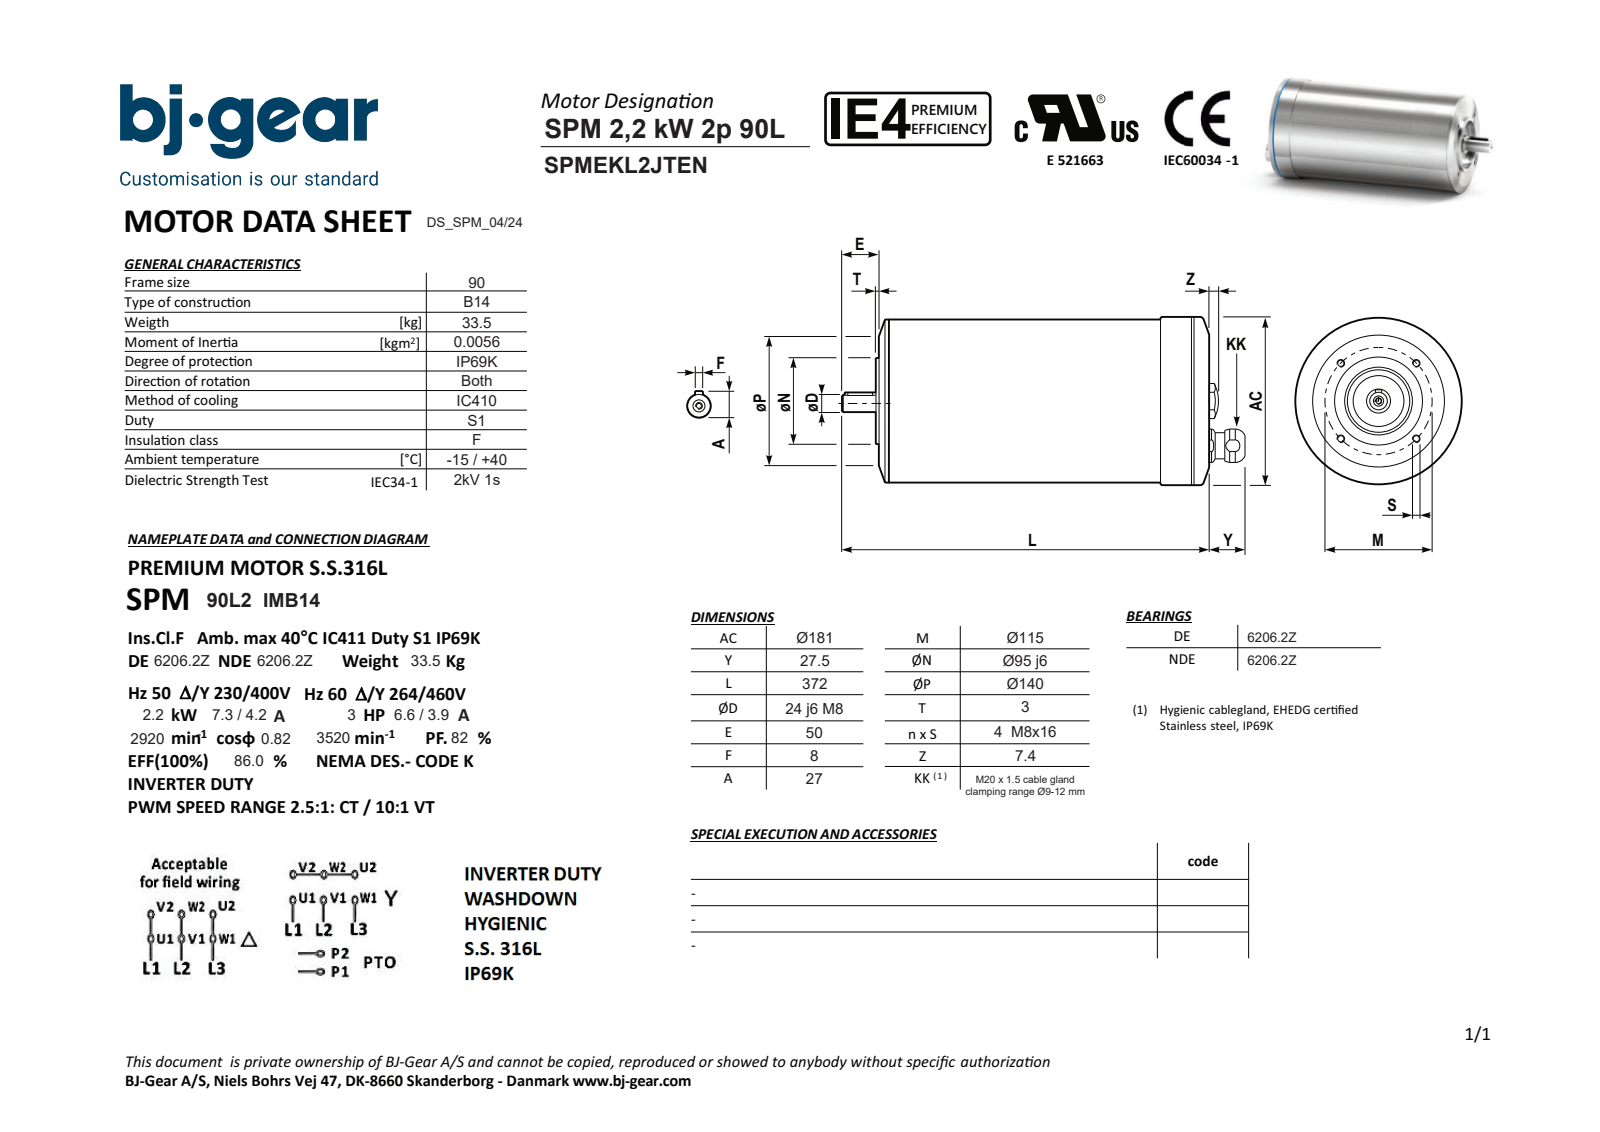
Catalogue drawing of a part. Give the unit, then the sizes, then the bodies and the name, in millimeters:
Units: millimetres
Overall size (bounding box): 399.5 × 181 × 181
Round holes (diameter × count): ⌀6.65 ×4, ⌀4.92 ×1, ⌀7 ×1, ⌀8.4 ×1, ⌀13.4 ×1, ⌀85 ×1
Round bosses / shafts (diameter × count): ⌀181 ×1, ⌀180.98 ×1, ⌀178 ×1, ⌀177.98 ×1, ⌀95 ×1, ⌀30 ×1, ⌀24 ×1, ⌀20 ×1
Partial cylindrical surfaces — rounded edges, fillets, slot ends (radius × count): R4 ×2, R12.8 ×1
Main face-to-face distances: 322, 6, 316, 325, 9, 3, 8, 24, 50, 372
Hole centre spacings: 57.5, 81.32, 43.11, 103.94, 115, 55
Volume: 8 014 000 mm³ · Surface area: 238 617 mm²
Bodies: 1 solid, 87 faces (30 planar, 32 cylindrical, 25 other)
Part name (STEP PRODUCT): SPMEKL2JTENN4KSA1-N---NNN
STEP written by: Solid Edge (AUTOMOTIVE_DESIGN)
